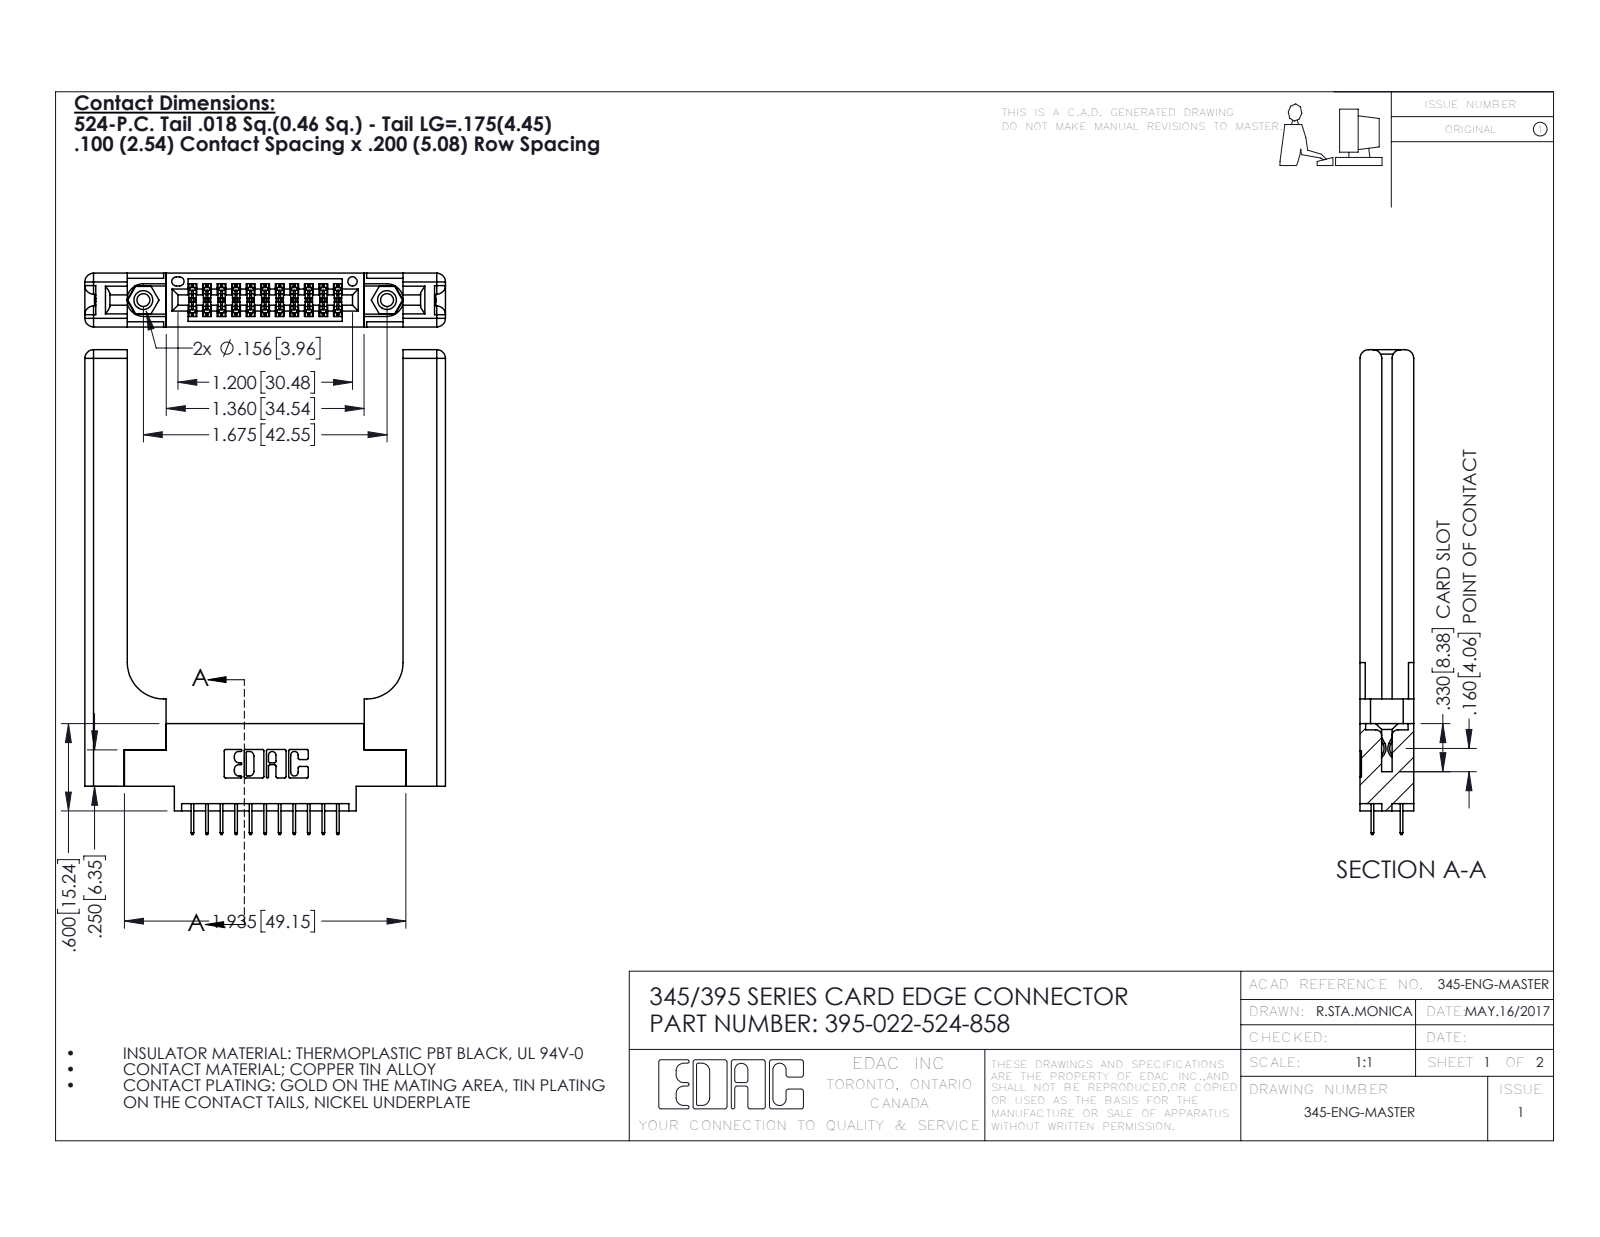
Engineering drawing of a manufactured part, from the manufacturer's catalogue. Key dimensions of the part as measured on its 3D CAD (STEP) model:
Part name (STEP PRODUCT): 345-250-001_345-250-001-102; 345-220-058_345-220-058; 345 Part_0.170 Offset - 0.156 Dia-TH; 395-022-524-858 (+1 more)
STEP written by: SolidWorks 2016 (CONFIG_CONTROL_DESIGN)
Units: inches
Bodies: 27 solids, 1574 faces (1090 planar, 424 cylindrical, 60 other)
Overall size (bounding box): 3.332 × 2.479 × 0.37
Volume: 0.864 in³ · Surface area: 20.02 in²
Round holes (diameter × count): ⌀0.089 ×2, ⌀0.125 ×2, ⌀0.156 ×2, ⌀0.064 ×1
Round bosses / shafts (diameter × count): ⌀0.155 ×2
Partial cylindrical surfaces — rounded edges, fillets, slot ends (radius × count): R0.006 ×33, R0.01 ×22, R0.06 ×16, R0.007 ×6, R0.031 ×6, R0.026 ×3, R0.014 ×2, R0.019 ×2
Main face-to-face distances: 0.37, 0.072, 0.15, 0.148, 0.077, 0.22, 0.298, 1.896, 0.225, 0.12
Hole centre spacings: 0.27, 1.443, 1.675
